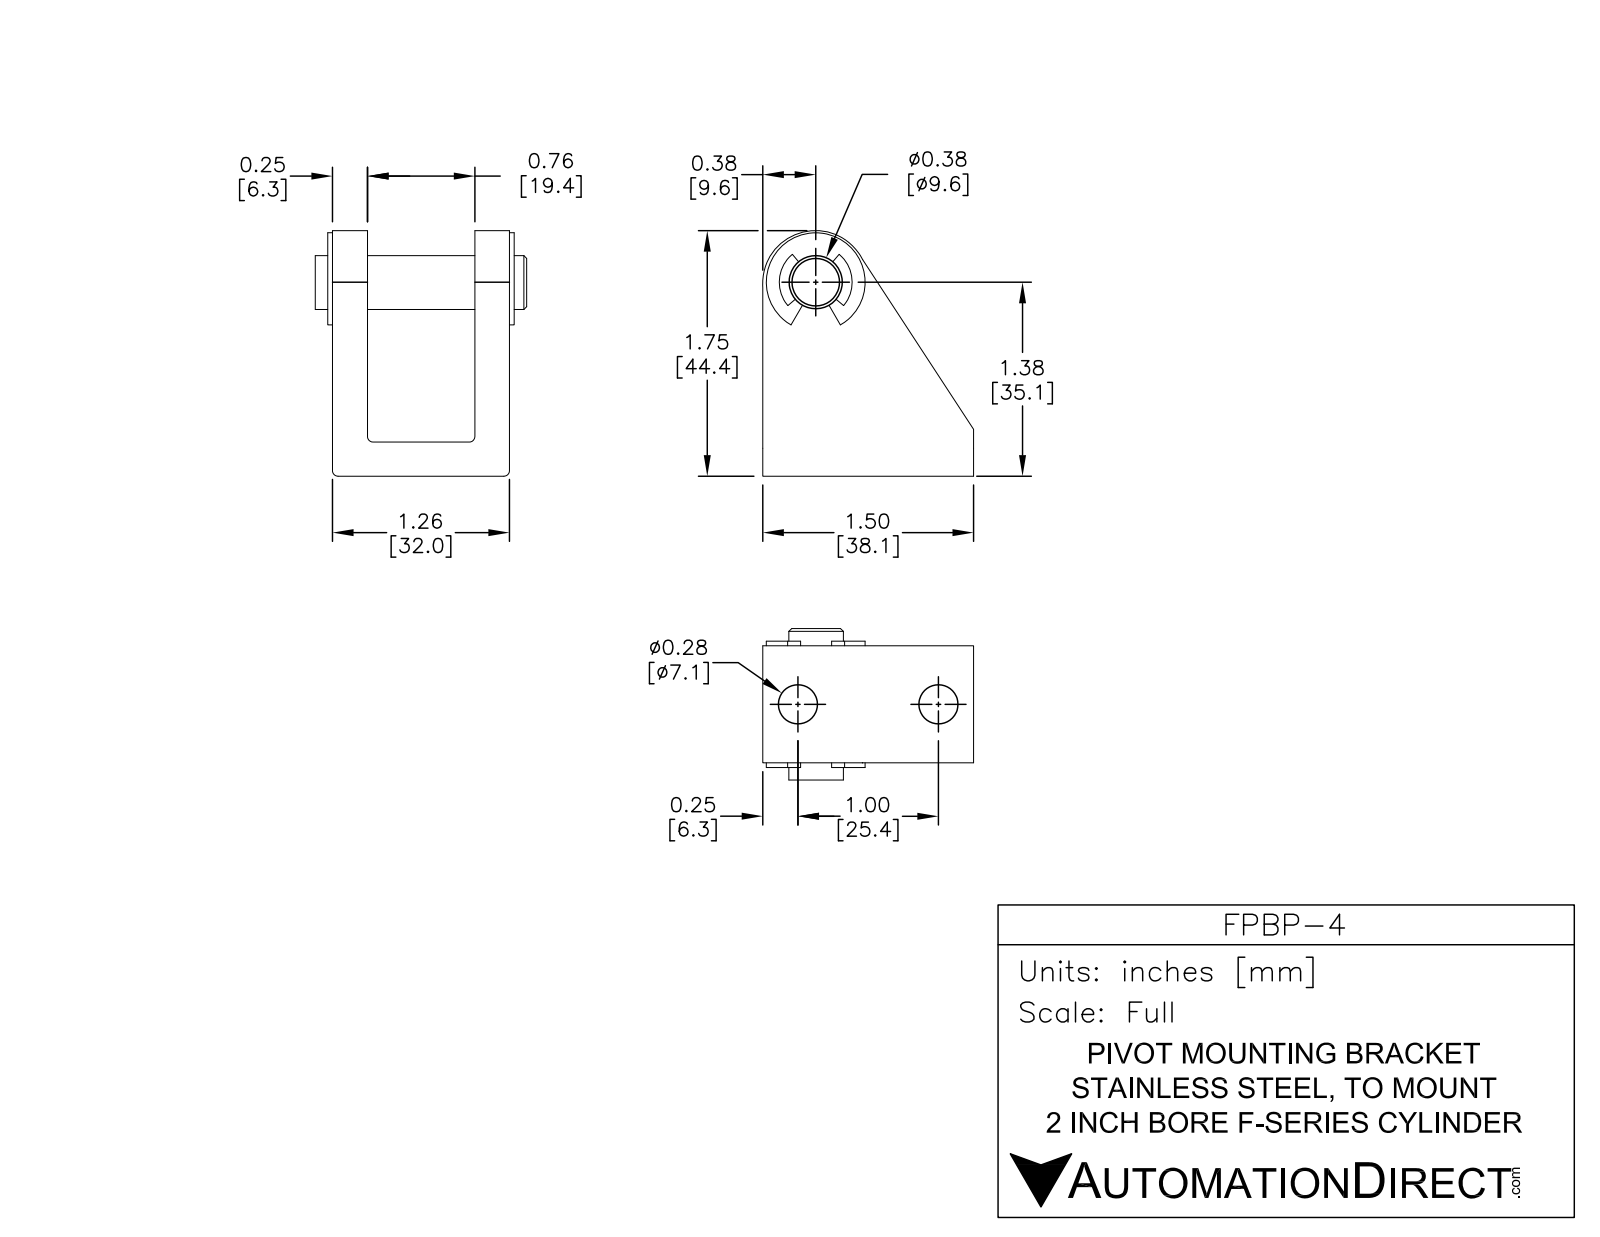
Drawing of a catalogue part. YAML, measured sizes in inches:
part_name: "FPBP-4"
step_written_by: "SolidWorks 2017 (AUTOMOTIVE_DESIGN)"
units: inches
bodies: {solids: 2, faces: 36, planar: 20, cylindrical: 16, other: 0}
overall_size: [1.75, 1.5, 1.5]
volume: 1.284
surface_area: 14.36
round_holes:
  - {diameter: 0.28, count: 2}
  - {diameter: 0.38, count: 1}
round_bosses_or_shafts:
  - {diameter: 0.375, count: 1}
partial_cylinders:
  - {radius: 0.03, count: 2}
  - {radius: 0.28, count: 2}
  - {radius: 0.38, count: 1}
face_to_face_distances: [0.25, 1.01, 0.76, 1.26, 1.5, 0.12, 0.37, 1.13, 1.38]
hole_center_spacings: [1]
